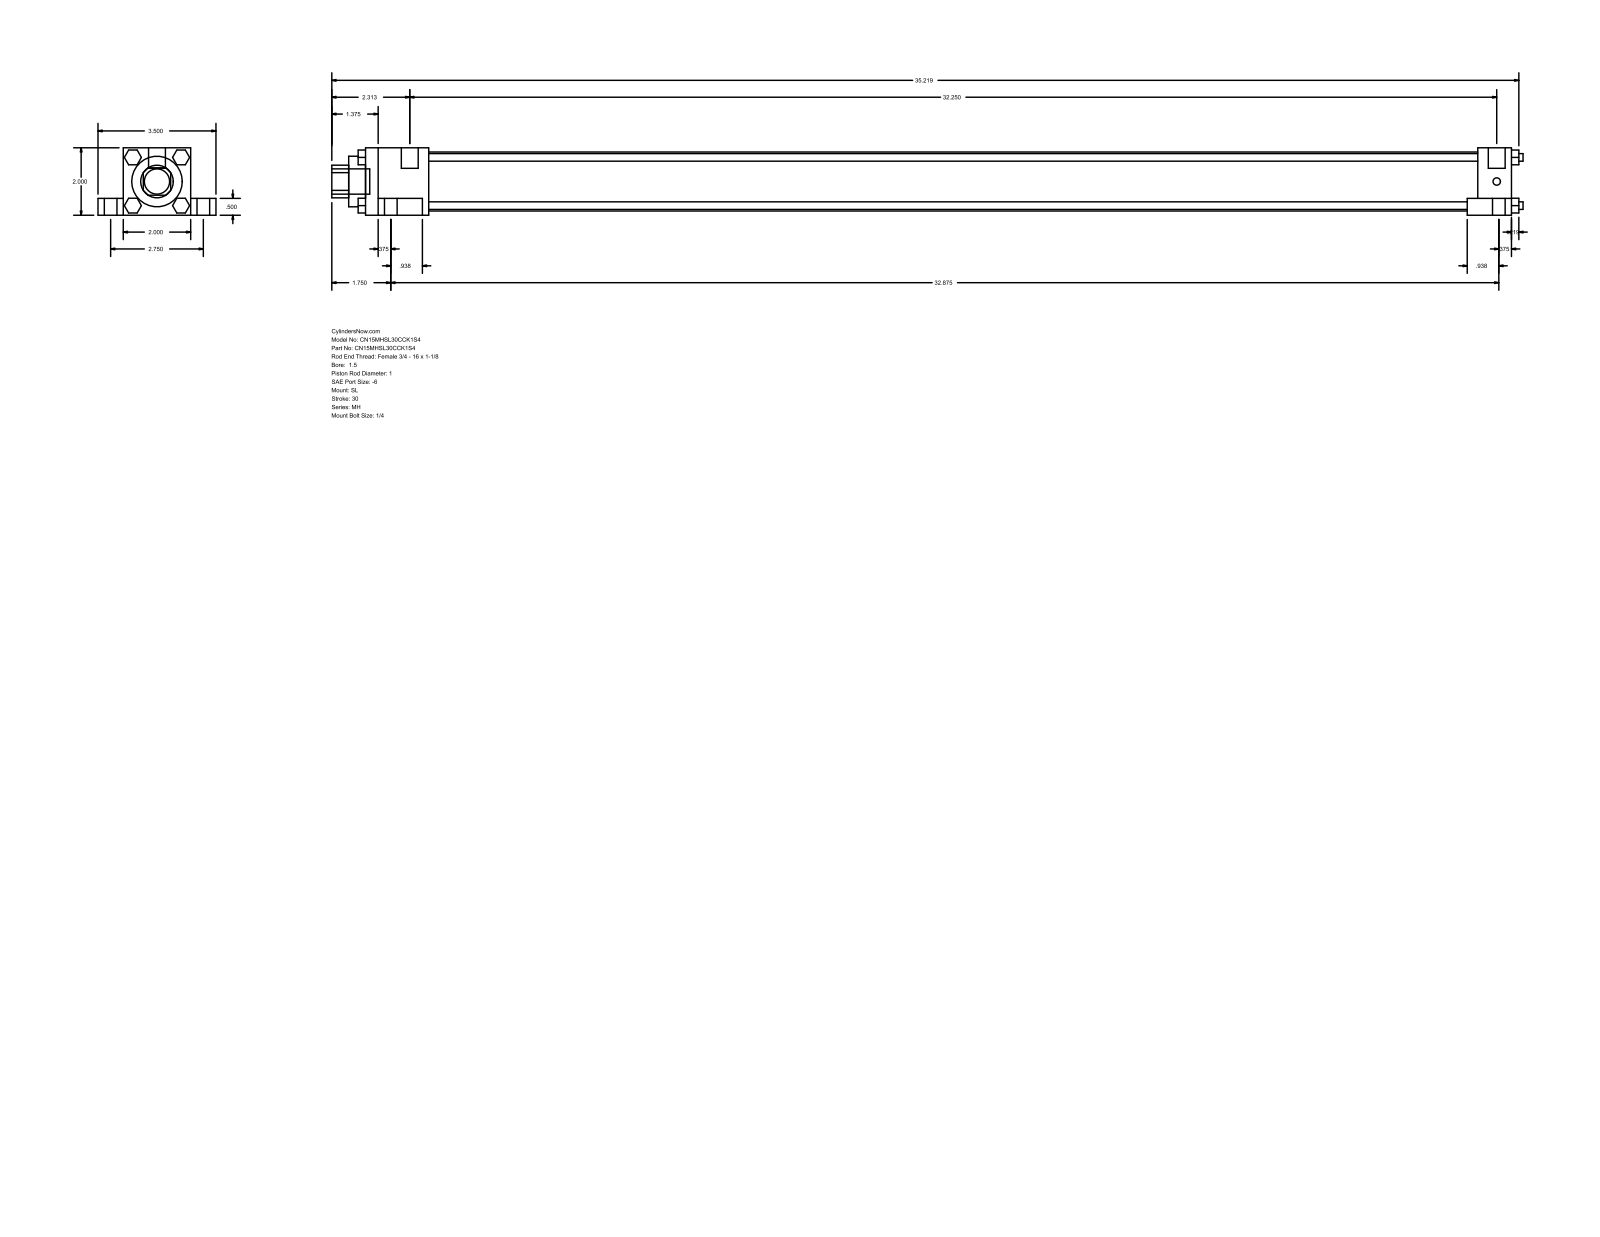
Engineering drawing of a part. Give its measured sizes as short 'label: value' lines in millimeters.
name: MH_SL__0150_1
written by: GSSL Pune (CONFIG_CONTROL_DESIGN)
unit: mm
bodies: 0 solids, 148 faces (112 planar, 36 cylindrical, 0 other)
size: 897.73 × 88.9 × 50.8
holes: 1× ⌀25.4, 1× ⌀38.1, 1× ⌀44.45
bosses: 4× ⌀15.88, 4× ⌀9.53, 4× ⌀5.71, 4× ⌀5.56, 2× ⌀12.7, 1× ⌀19.05
rounds: 1× R12.29
face distances: 50.8, 12.7, 38.1, 19.05, 69.85, 863.6, 25.4, 9.52, 33.34, 820.74
